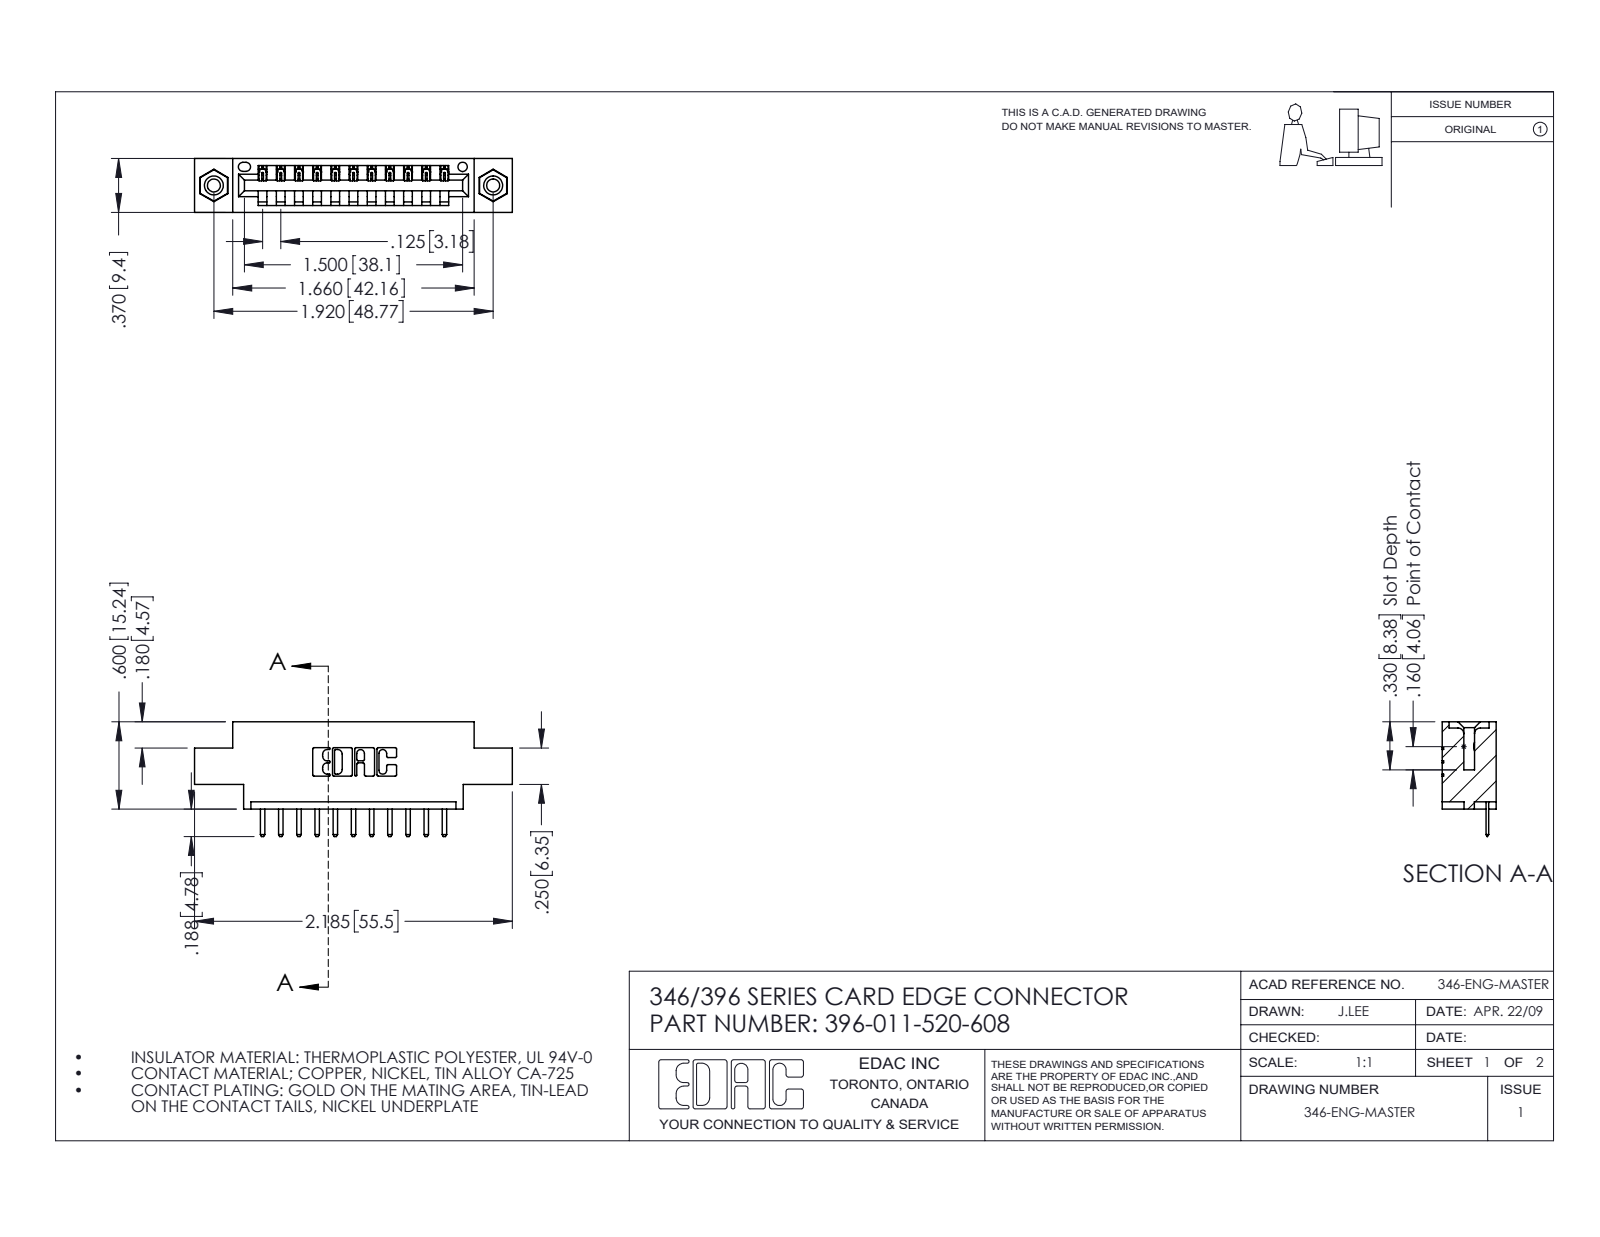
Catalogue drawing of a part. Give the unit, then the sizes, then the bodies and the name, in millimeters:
Units: millimetres
Overall size (bounding box): 55.5 × 20 × 9.4
Round holes (diameter × count): ⌀2.3 ×2, ⌀3.2 ×2, ⌀4 ×2, ⌀1.6 ×1
Round bosses / shafts (diameter × count): ⌀3.9 ×2
Partial cylindrical surfaces — rounded edges, fillets, slot ends (radius × count): R0.3 ×24, R0.2 ×22, R0.3 ×22, R0.2 ×6, R0.8 ×6, R0.7 ×3, R0.8 ×2, R1 ×2
Main face-to-face distances: 6.4, 9.4, 1.2, 8.2, 5.6, 3.8, 2.5, 4.4, 1.8, 7.6
Hole centre spacings: 6.2, 43.6, 48.8
Volume: 4 900 mm³ · Surface area: 5 874 mm²
Bodies: 14 solids, 868 faces (574 planar, 278 cylindrical, 16 other)
Part name (STEP PRODUCT): 346 Part_0.170 Offset - 0.156 Dia-TI; 396-011-520-608; 345-250-001_345-250-003-102; 345-292-001_345-293-120
STEP written by: SolidWorks 2016 (CONFIG_CONTROL_DESIGN)
